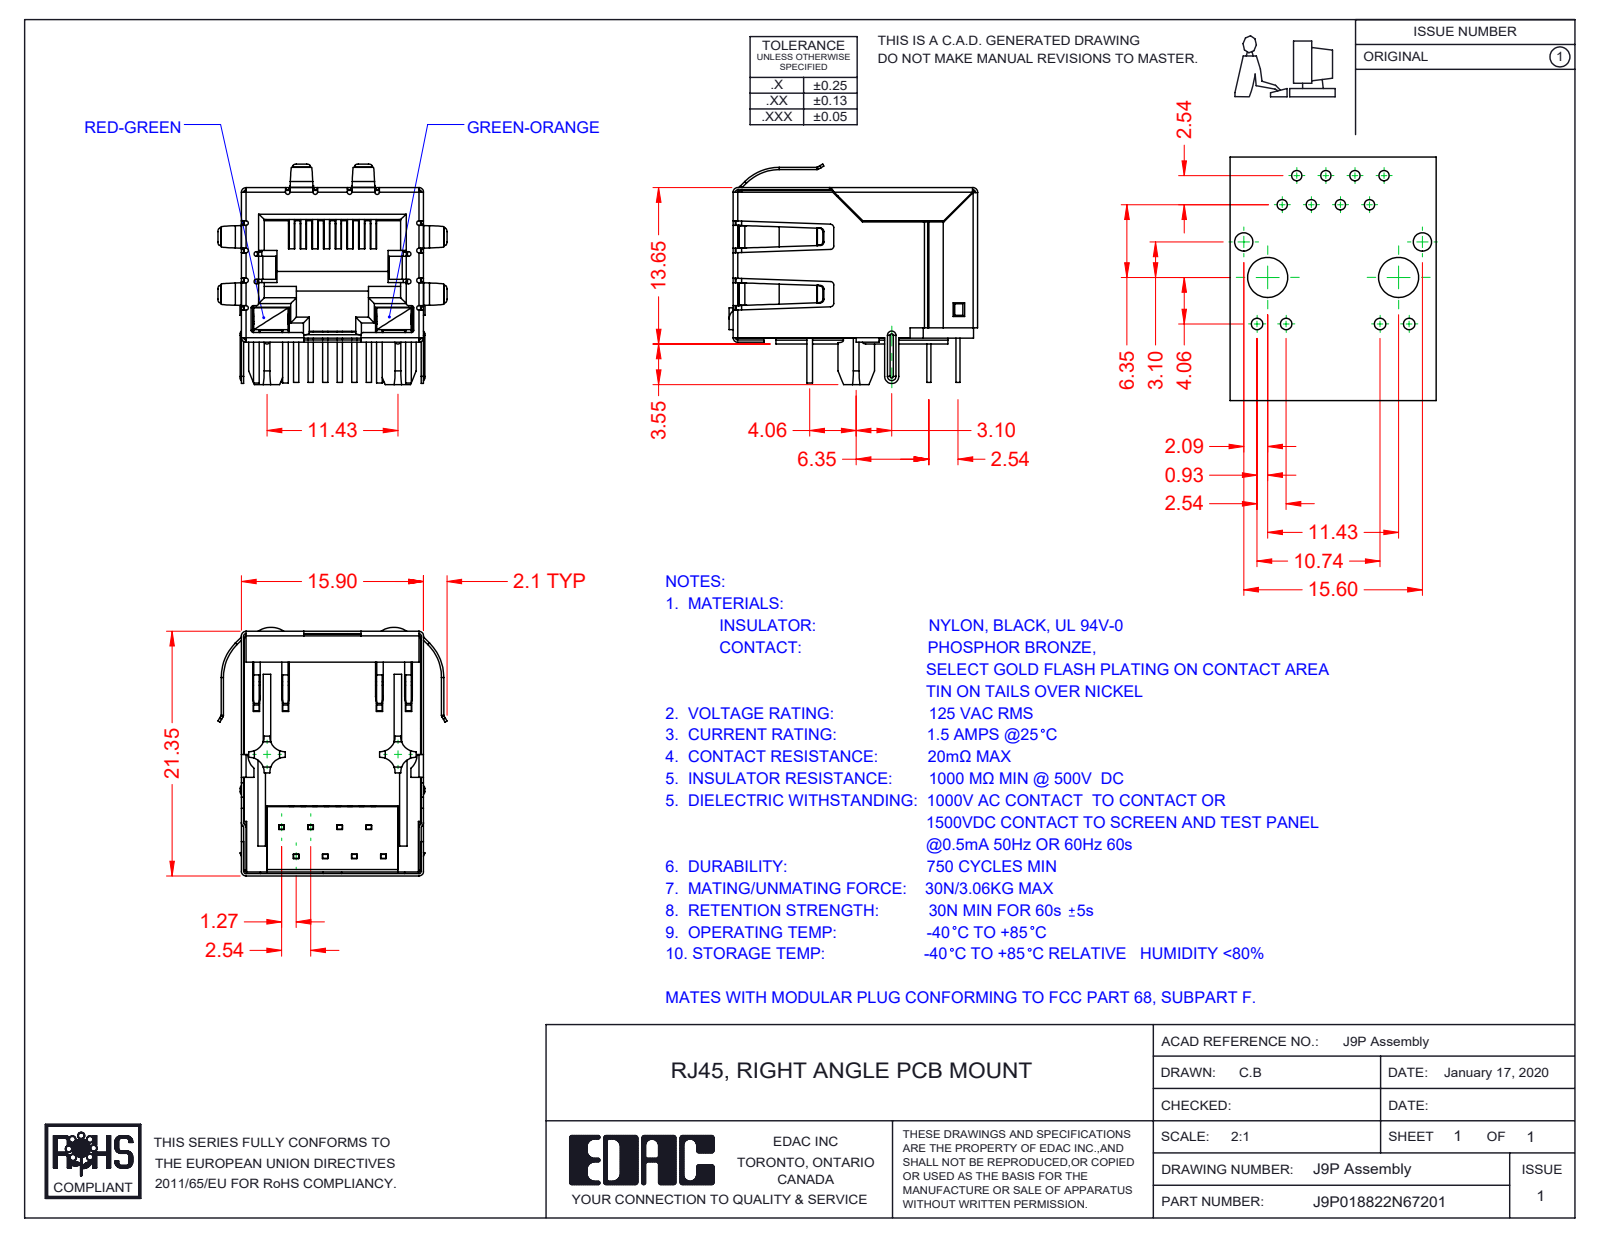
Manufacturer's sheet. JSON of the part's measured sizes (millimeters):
{"part_name": "9P-LED Shield; 9P-LED LED RH_7-Green-Orange; 9P-LED Contact Lock; 9P-LED Insulator (+4 more)", "step_written_by": "SolidWorks 2016 (CONFIG_CONTROL_DESIGN)", "units": "millimeters", "bodies": {"solids": 13, "faces": 1476, "planar": 1042, "cylindrical": 340, "other": 94}, "overall_size": [21.7, 20, 19.25], "volume_mm3": 2687, "surface_area_mm2": 7515, "partial_cylinders_radius": [[0.2, 39], [0.5, 22], [0.3, 20], [0.4, 16], [1.3, 8], [0.23, 5], [0.11, 4], [0.31, 4]], "face_to_face_distances": [15.45, 15.7, 15.65, 0.35, 0.54, 15.5, 12.36, 0.6, 1.4, 0.59]}
